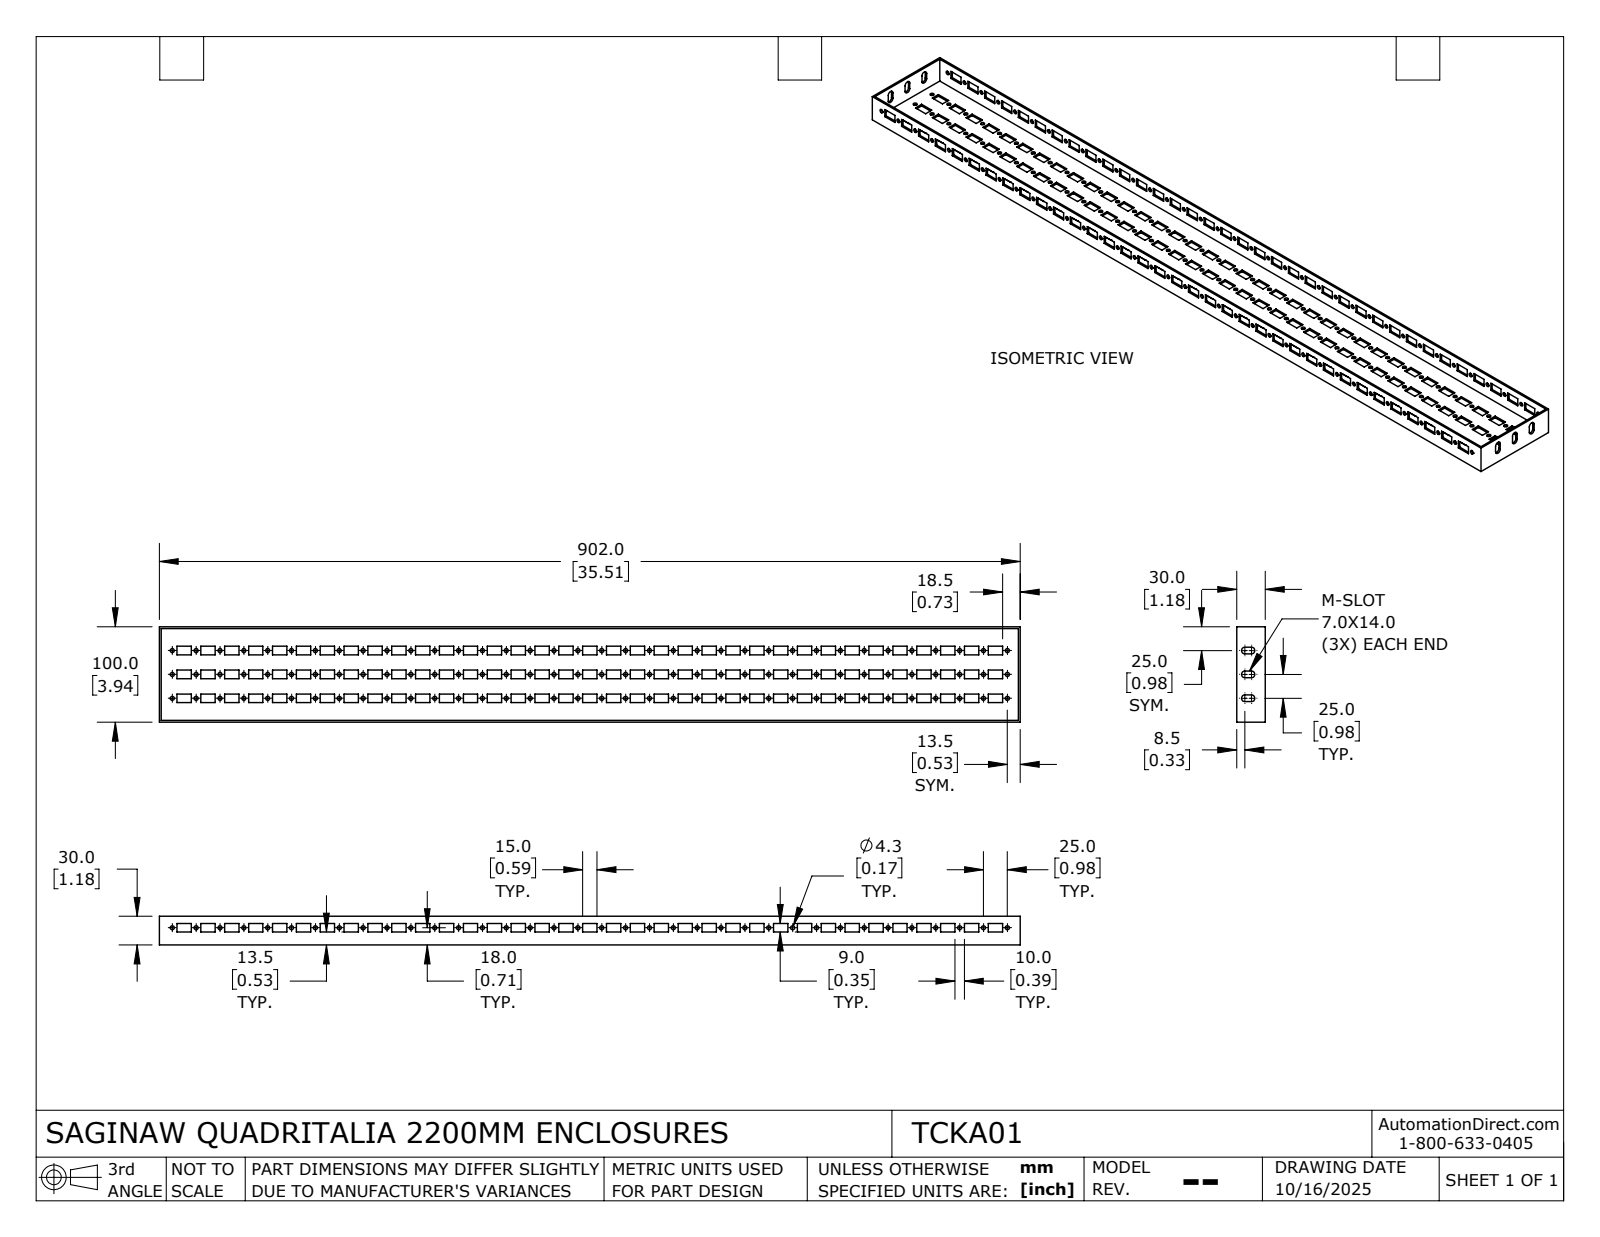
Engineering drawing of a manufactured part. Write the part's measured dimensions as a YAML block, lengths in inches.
part_name: "TCKA01"
step_written_by: "SolidWorks 2024 (AUTOMOTIVE_DESIGN)"
units: inches
bodies: {solids: 1, faces: 915, planar: 723, cylindrical: 192, other: 0}
overall_size: [35.512, 3.937, 1.181]
volume: 14.57
surface_area: 410.5
round_holes:
  - {diameter: 0.167, count: 144}
partial_cylinders:
  - {radius: 0.138, count: 6}
face_to_face_distances: [0.079, 3.858, 3.937, 3.78, 0.984, 0.354, 35.433, 0.807, 1.181, 1.102]
hole_center_spacings: [0.984, 1.969, 2.201, 2.953, 3.937, 4.921, 1.392, 5.906]
